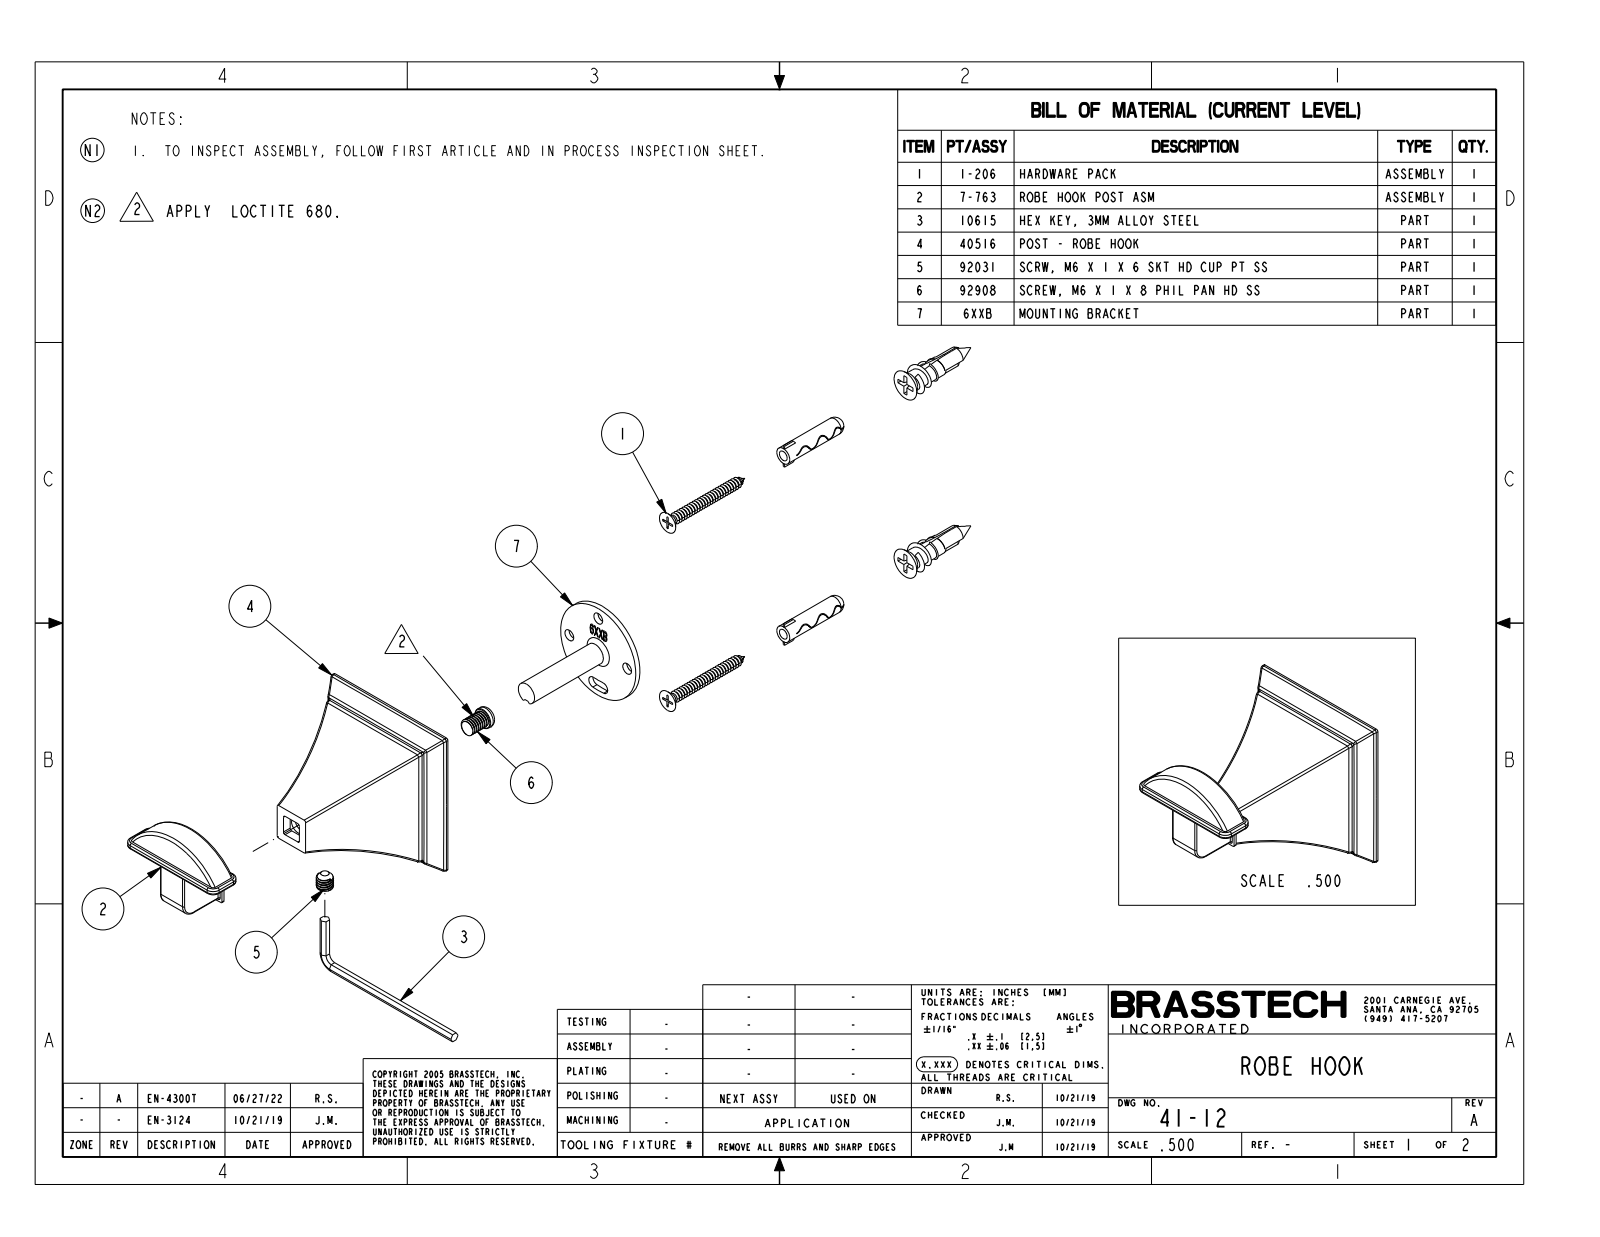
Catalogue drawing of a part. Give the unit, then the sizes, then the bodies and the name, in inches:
Units: inches
Overall size (bounding box): 2.721 × 2.224 × 2.224
Partial cylindrical surfaces — rounded edges, fillets, slot ends (radius × count): R0.02 ×16, R0.027 ×8, R0.03 ×4, R0.118 ×4, R0.039 ×1, R0.197 ×1, R0.984 ×1
Main face-to-face distances: 2.662, 2.268, 0.394, 0.46, 0.392, 2.66, 0.71, 0.877, 1.347, 0.882
Volume: 3.955 in³ · Surface area: 20.46 in²
Bodies: 1 solid, 133 faces (25 planar, 35 cylindrical, 73 other)
Part name (STEP PRODUCT): 41-12
STEP written by: CREO PARAMETRIC BY PTC INC, 2019352 (CONFIG_CONTROL_DESIGN)
